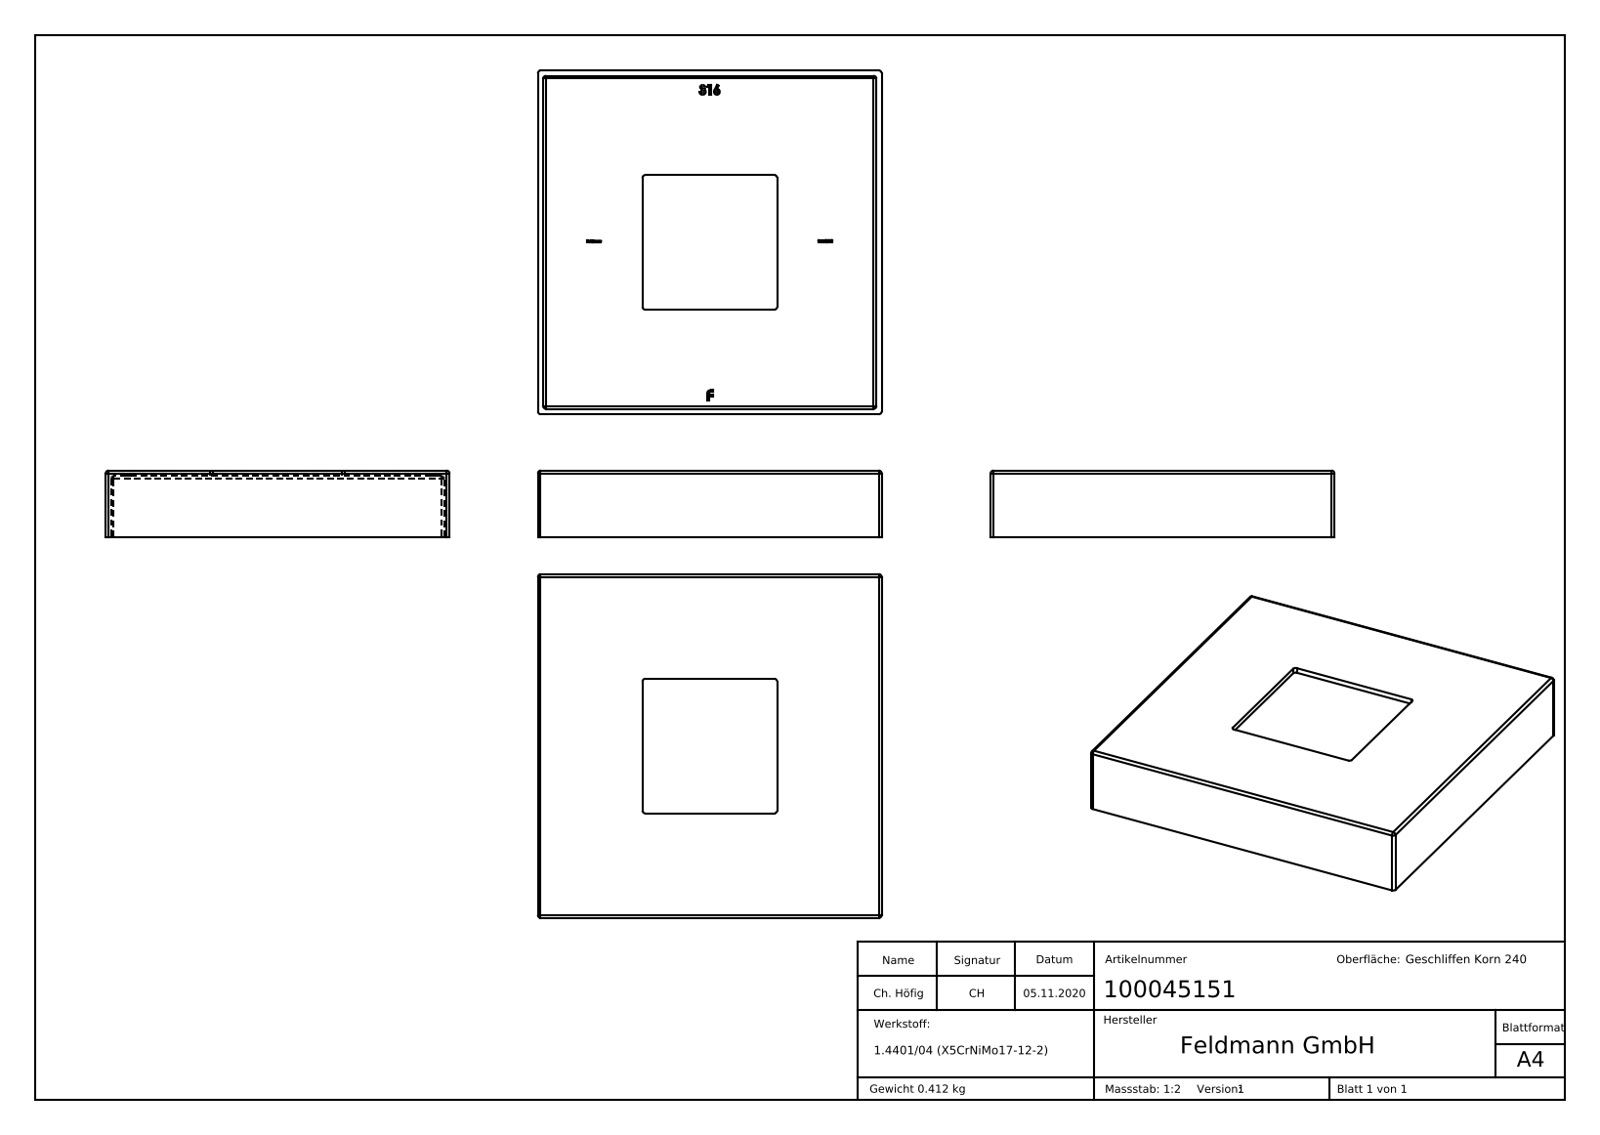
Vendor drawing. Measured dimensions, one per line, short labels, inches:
name: 100045151
written by: SolidWorks 2018 (CONFIG_CONTROL_DESIGN)
unit: in
bodies: 1 solid, 305 faces (163 planar, 20 cylindrical, 122 other)
size: 5.079 × 5.079 × 0.984
volume: 3.145 in³; area: 81.34 in²
rounds: 20× R0.039
face distances: 0.079, 5, 5.079, 4.921, 0.906, 0.984, 1.545, 3.533, 1.467, 3.455
